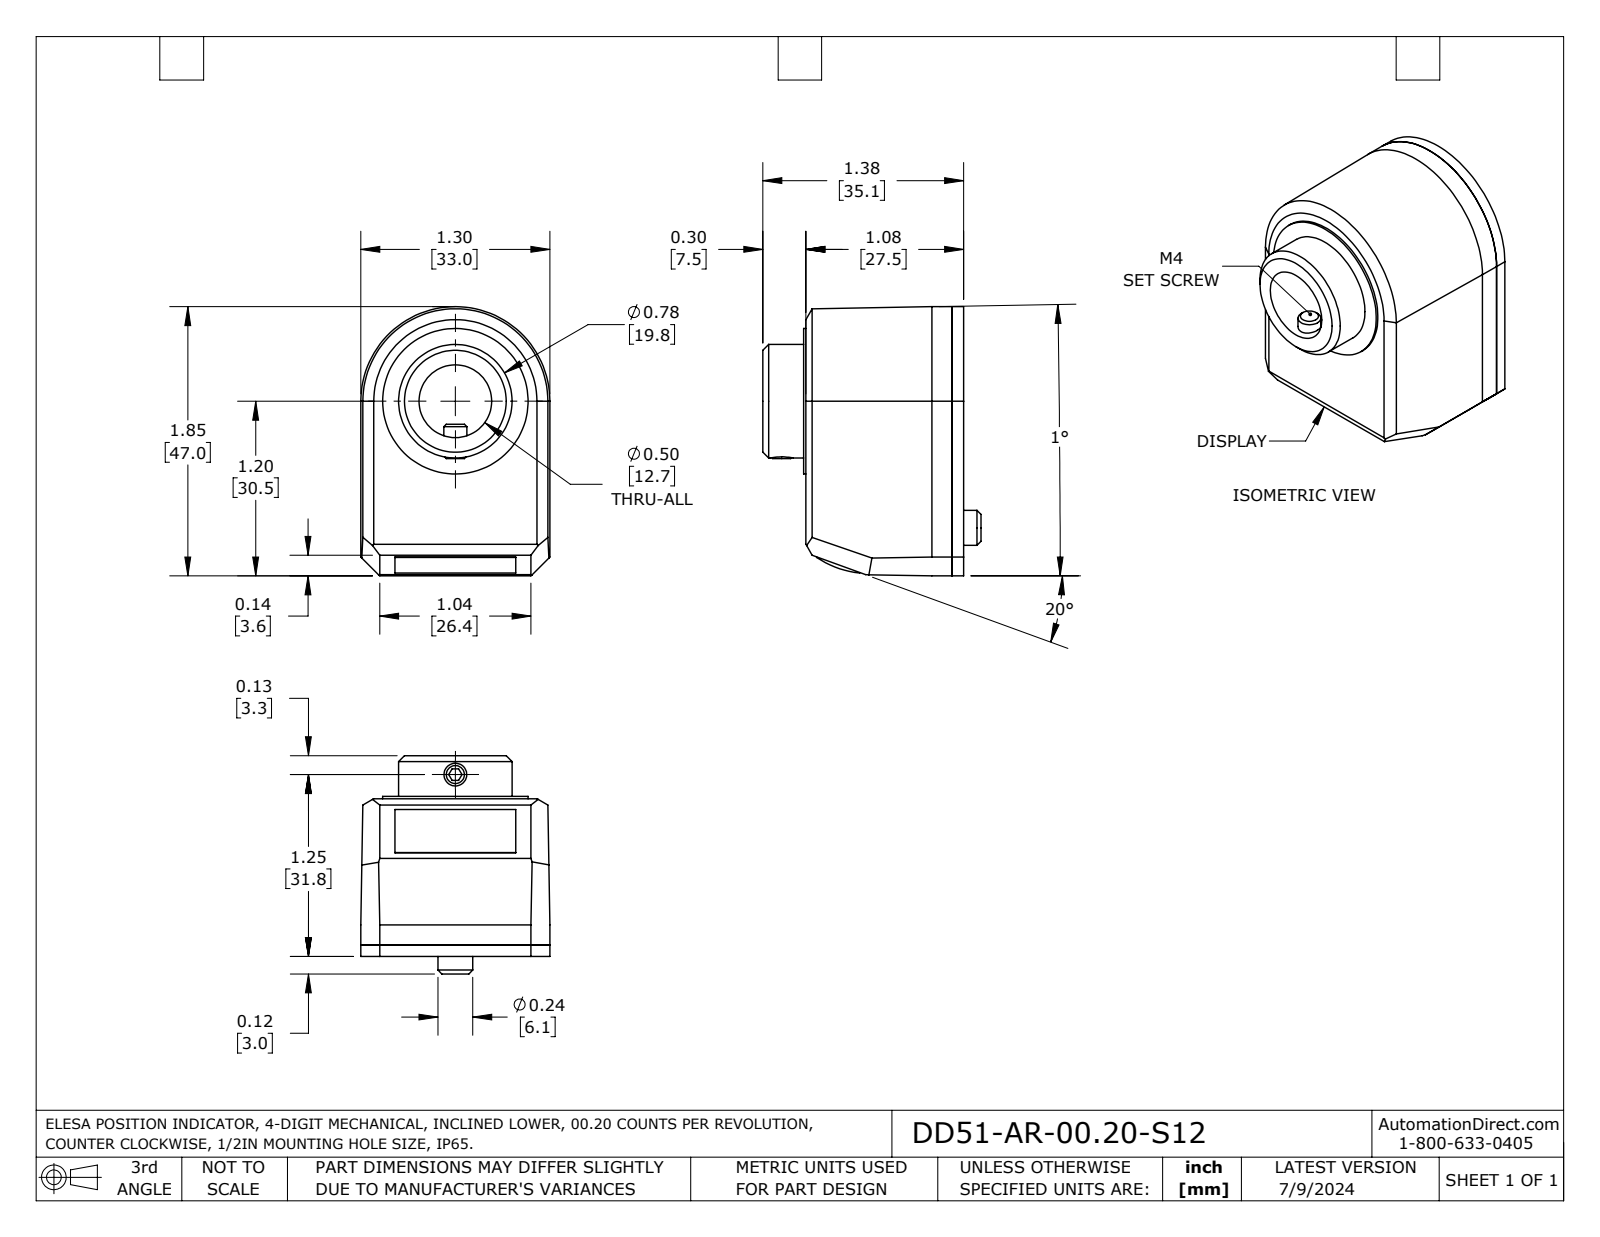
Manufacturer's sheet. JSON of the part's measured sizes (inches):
{"part_name": "DD51-AR-INCH", "step_written_by": "SolidWorks 2023 (AUTOMOTIVE_DESIGN)", "units": "inches", "bodies": {"solids": 4, "faces": 77, "planar": 59, "cylindrical": 12, "other": 6}, "overall_size": [1.85, 1.5, 1.3], "volume_in3": 2.036, "surface_area_in2": 20.14, "round_holes": [[0.157, 1], [0.5, 1], [0.78, 1], [1.08, 1]], "round_bosses_or_shafts": [[1, 1], [0.24, 1], [0.157, 1]], "partial_cylinders_radius": [[0.65, 1], [0.662, 1]], "face_to_face_distances": [0.08, 1.004, 1.084, 0.864, 0.14, 0.22, 1.3, 0.016, 0.88, 1.02]}
